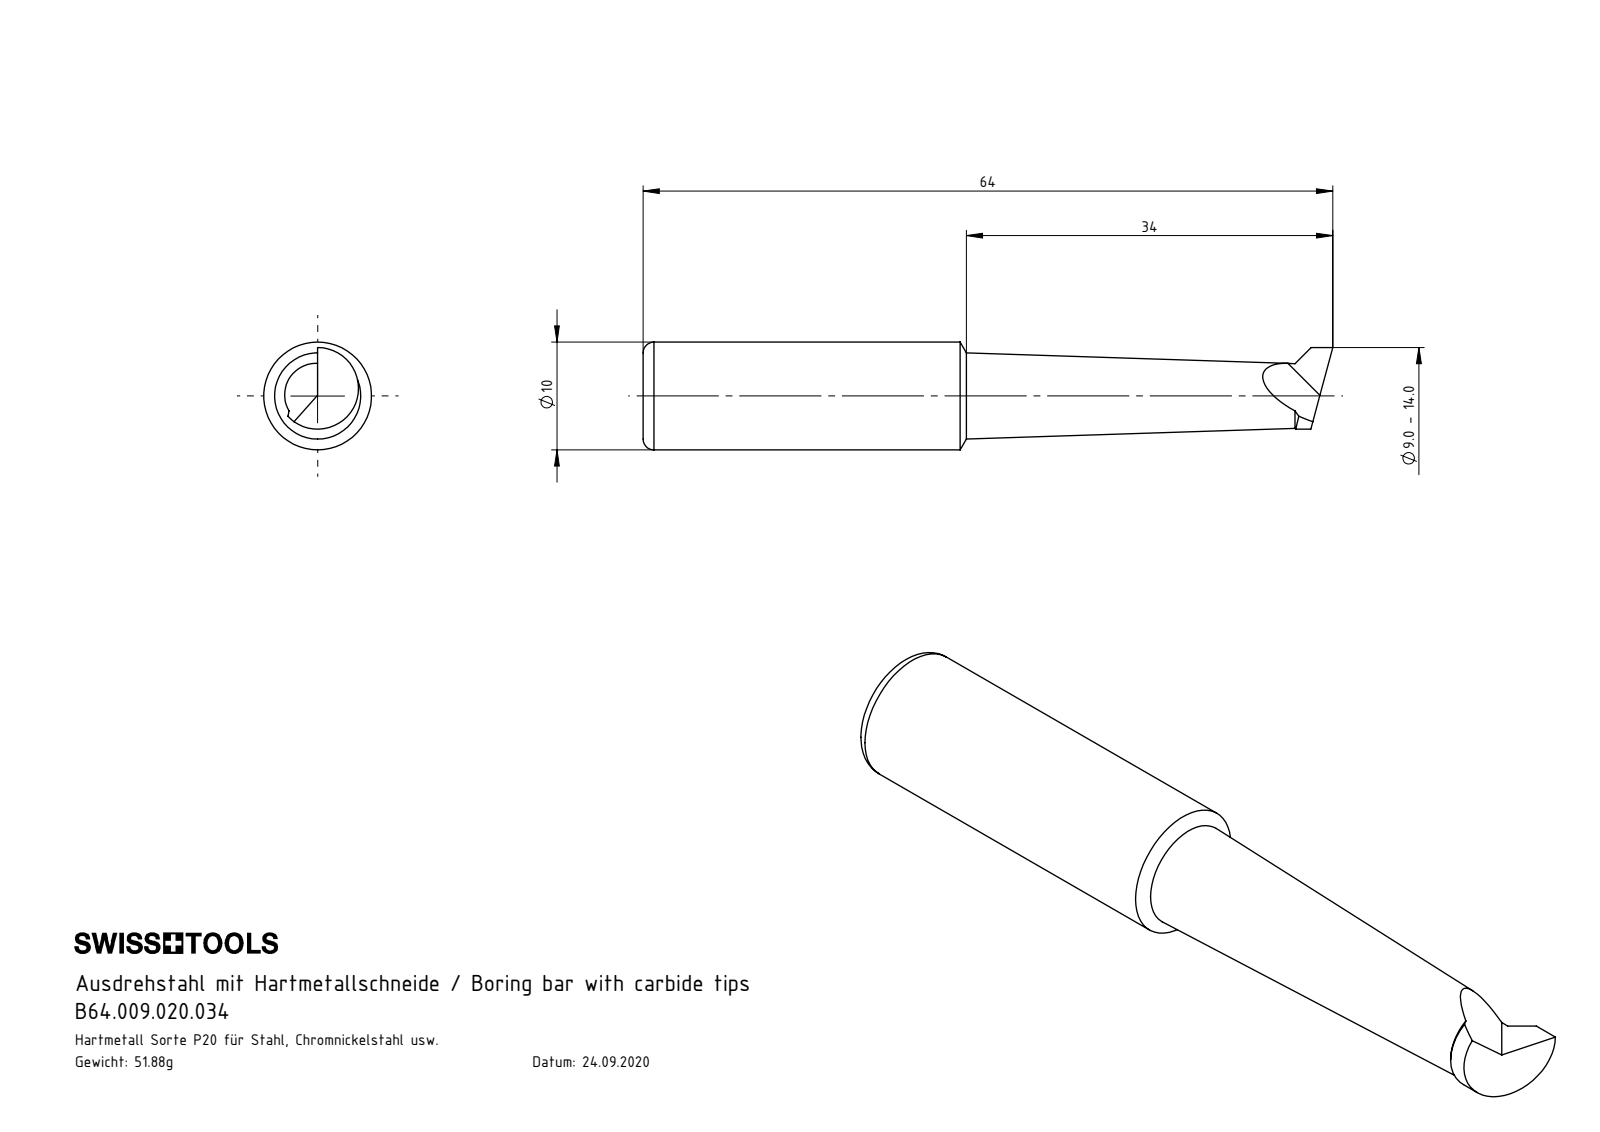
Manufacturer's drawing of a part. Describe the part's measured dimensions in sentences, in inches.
The part is named "B64.009.020.034". Its 3-D file was written by "SolidWorks 2022 (CONFIG_CONTROL_DESIGN)". It is 1 solid with 14 faces: 4 planar, 3 cylindrical and 7 other. Overall it measures 2.52 by 0.394 by 0.394 inches. Its volume is 0.218 cubic inches and its surface area 2.753 square inches. Round bosses or shafts: 1 of diameter 0.394. Partial cylindrical surfaces (rounded edges, fillets, slot ends): 1 of radius 0.149.
